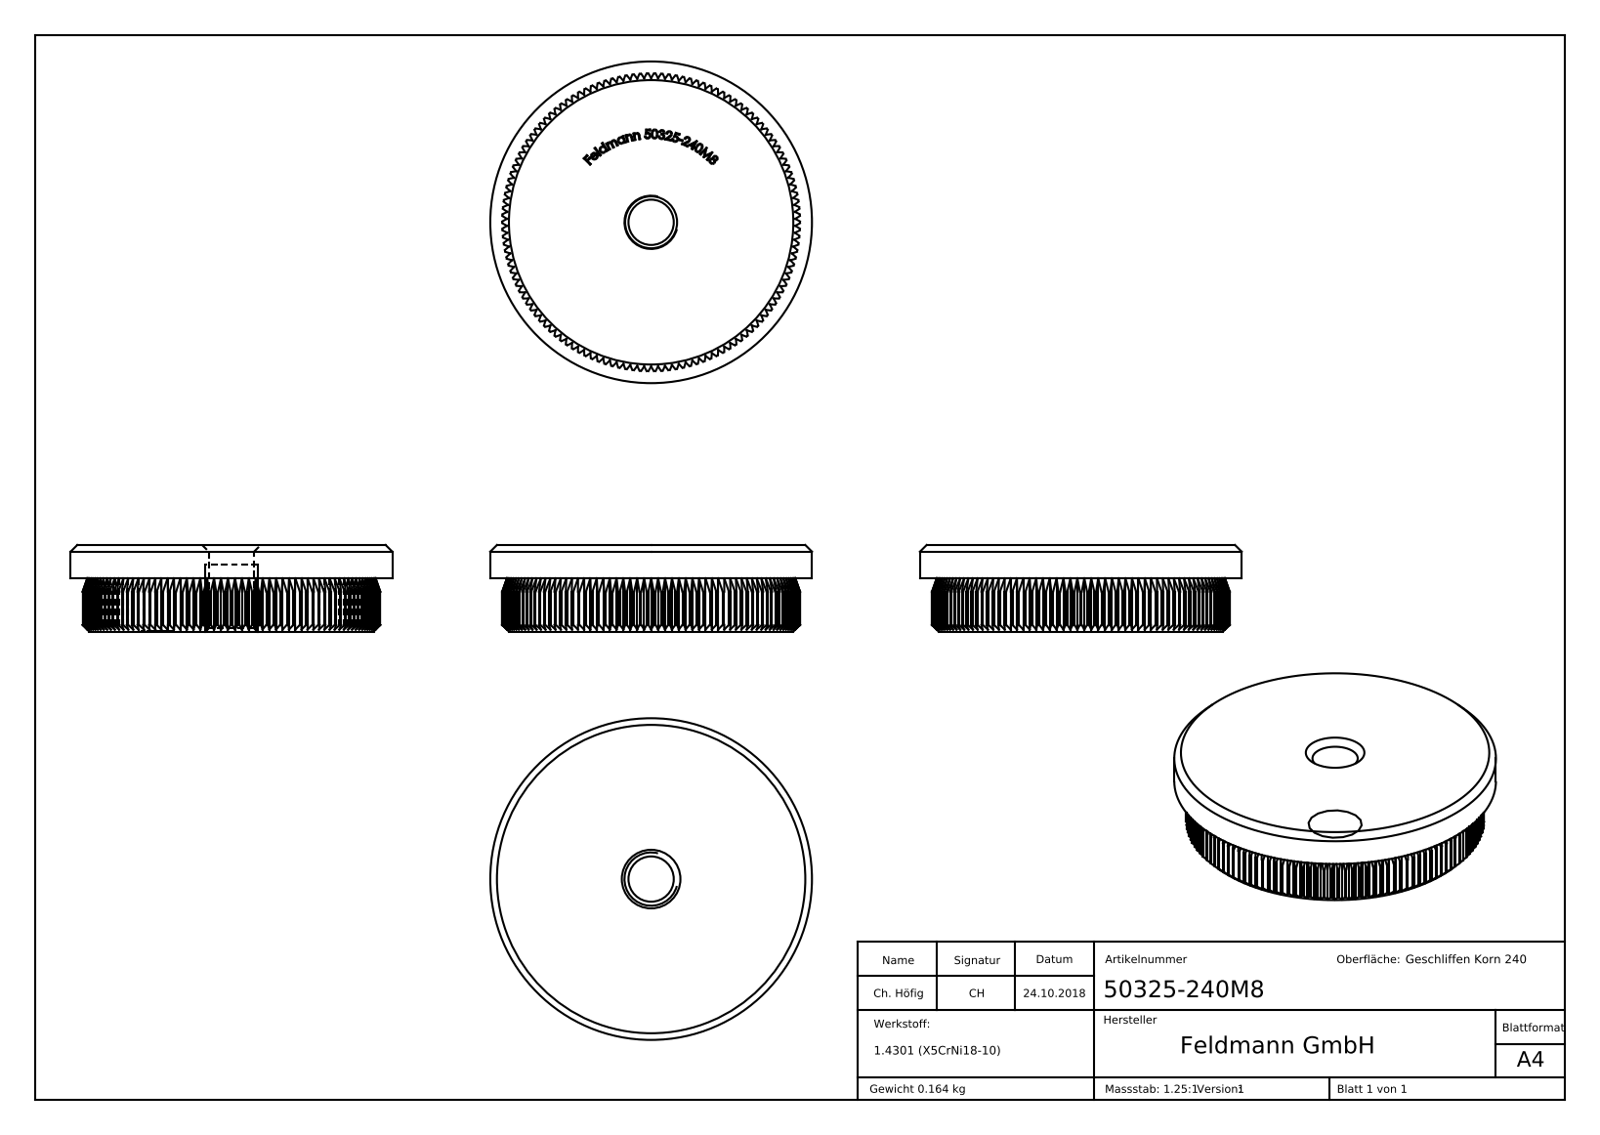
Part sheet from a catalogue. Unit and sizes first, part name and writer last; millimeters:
Units: millimetres
Overall size (bounding box): 48.3 × 48.3 × 13
Round holes (diameter × count): ⌀6.8 ×1
Round bosses / shafts (diameter × count): ⌀48.3 ×1
Partial cylindrical surfaces — rounded edges, fillets, slot ends (radius × count): R22.35 ×1
Main face-to-face distances: 13, 8, 5, 21.66, 21.64, 21.68, 21.62, 7.9, 12.9, 0.54
Volume: 20 771 mm³ · Surface area: 6 324 mm²
Bodies: 1 solid, 821 faces (410 planar, 134 cylindrical, 277 other)
Part name (STEP PRODUCT): 50325-240M8
STEP written by: SolidWorks 2015 (CONFIG_CONTROL_DESIGN)
